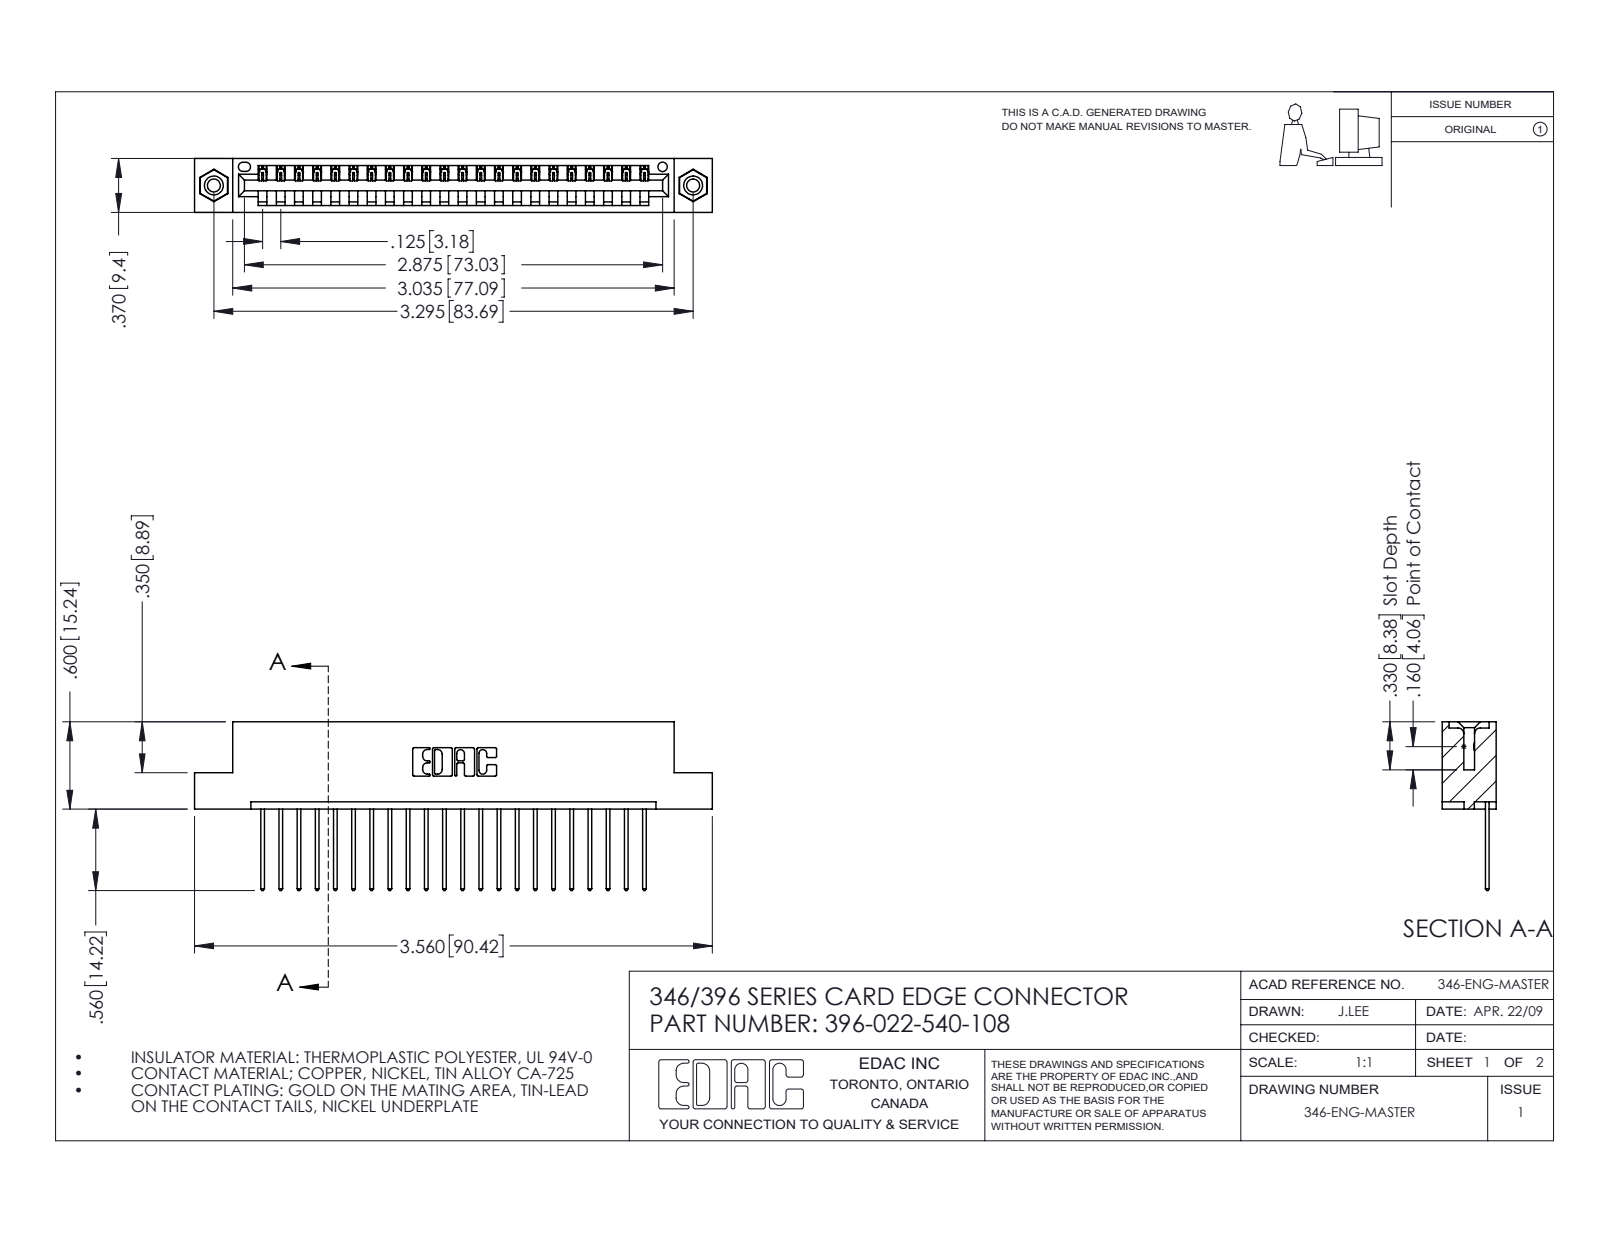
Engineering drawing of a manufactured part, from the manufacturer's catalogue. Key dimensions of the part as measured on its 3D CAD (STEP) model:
Part name (STEP PRODUCT): 396-022-540-108; 345-250-001_345-250-003-102; 346 Part_Flush Mounting Lugs - 0.156 Dia-TI; 345-292-001_345-293-140
STEP written by: SolidWorks 2016 (CONFIG_CONTROL_DESIGN)
Units: inches
Bodies: 25 solids, 1458 faces (988 planar, 454 cylindrical, 16 other)
Overall size (bounding box): 3.56 × 1.16 × 0.37
Volume: 0.521 in³ · Surface area: 16.58 in²
Round holes (diameter × count): ⌀0.089 ×2, ⌀0.125 ×2, ⌀0.156 ×2, ⌀0.064 ×1
Round bosses / shafts (diameter × count): ⌀0.155 ×2
Partial cylindrical surfaces — rounded edges, fillets, slot ends (radius × count): R0.006 ×44, R0.01 ×44, R0.01 ×22, R0.007 ×6, R0.031 ×6, R0.026 ×3, R0.031 ×2, R0.04 ×2
Main face-to-face distances: 0.048, 0.322, 0.25, 0.37, 0.072, 0.298, 0.025, 0.148, 0.222, 0.1
Hole centre spacings: 0.246, 3.087, 3.295
